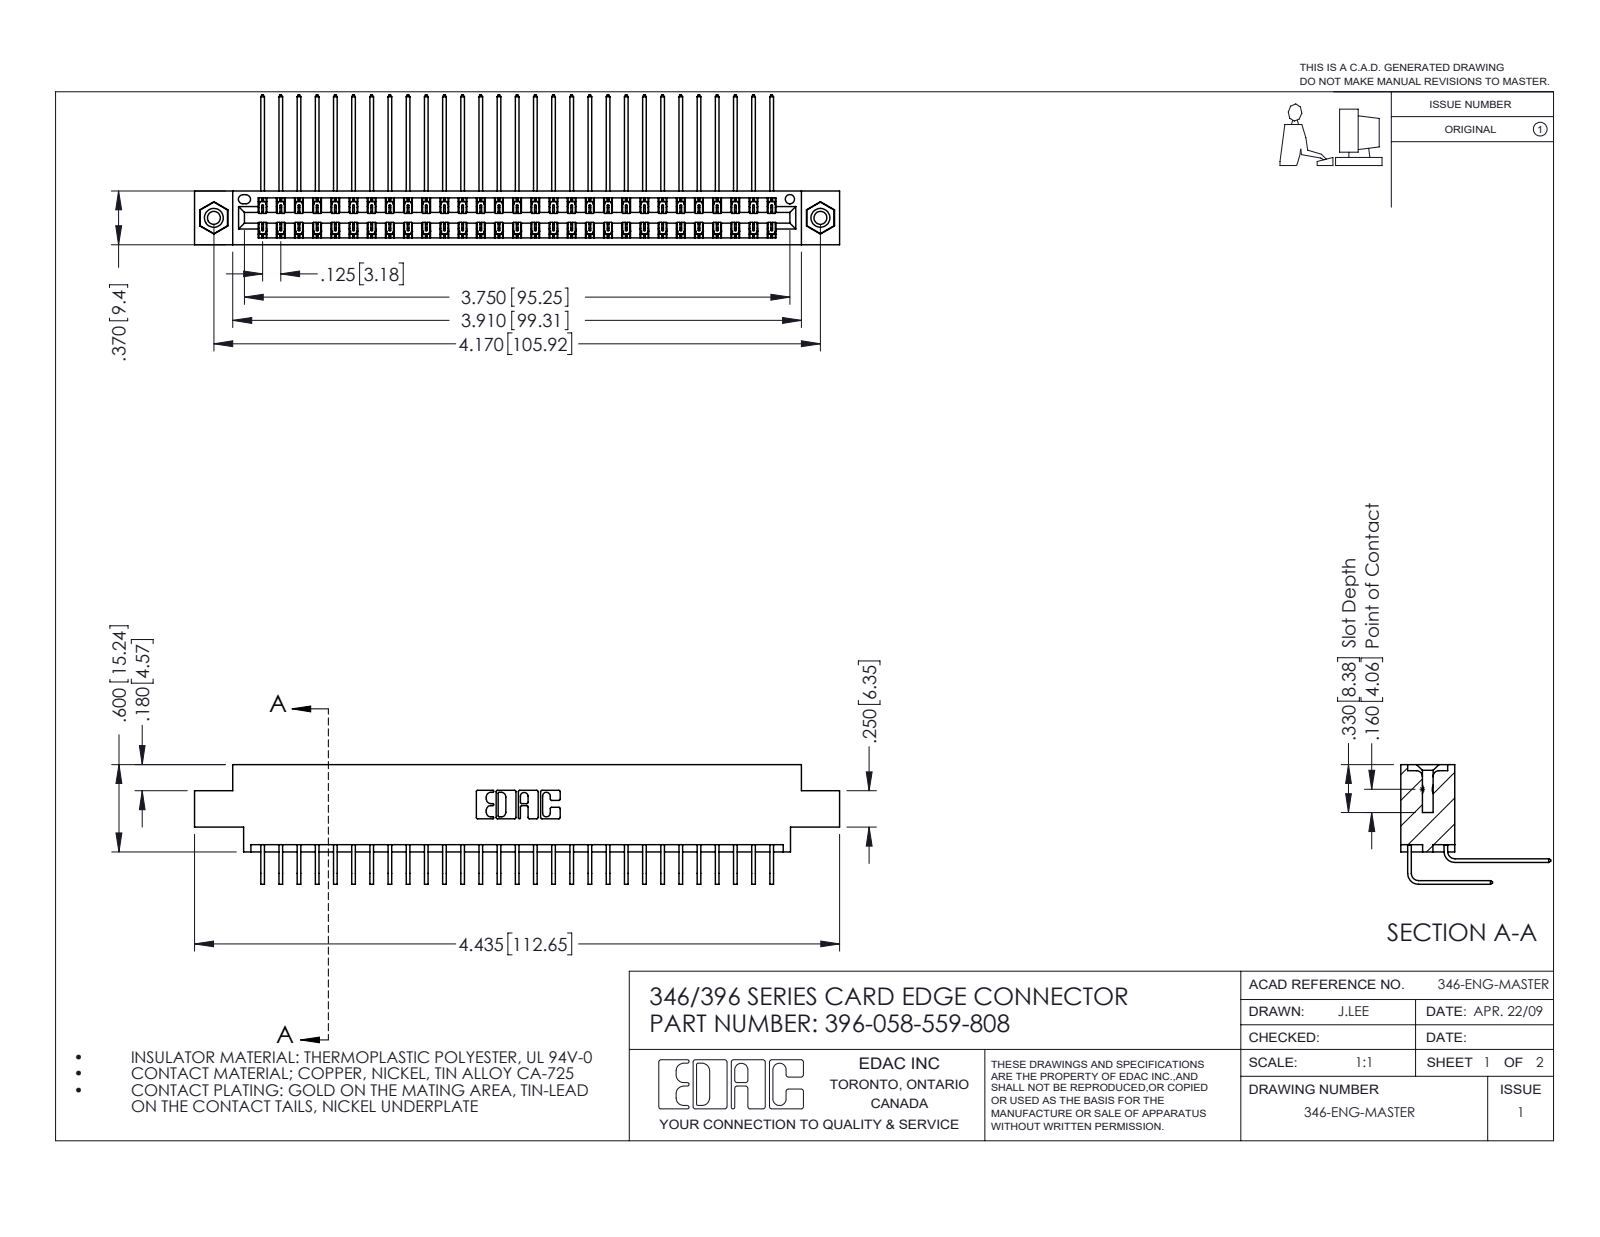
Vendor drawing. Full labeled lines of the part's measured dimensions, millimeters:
Part name (STEP PRODUCT): 346 Part_0.170 Offset - 0.156 Dia-TI; 396-058-559-808; 345-292-001_558 559 Tail - 1; 345-292-001_559 Tail - 2 (+1 more)
STEP written by: SolidWorks 2016 (CONFIG_CONTROL_DESIGN)
Units: millimetres
Bodies: 61 solids, 3318 faces (2258 planar, 1044 cylindrical, 16 other)
Overall size (bounding box): 112.6 × 26.2 × 20.9
Volume: 11 100 mm³ · Surface area: 16 800 mm²
Round holes (diameter × count): ⌀2.3 ×2, ⌀3.2 ×2, ⌀4 ×2, ⌀1.6 ×1
Round bosses / shafts (diameter × count): ⌀3.9 ×2
Partial cylindrical surfaces — rounded edges, fillets, slot ends (radius × count): R0.2 ×87, R0.3 ×22, R0.2 ×6, R0.8 ×6, R0.7 ×3, R0.4 ×2, R0.6 ×2, R0.6 ×2
Main face-to-face distances: 1.2, 8.2, 0.6, 9.4, 6.4, 1.8, 7.6, 7, 5.6, 3.8
Hole centre spacings: 6.2, 100.6, 105.9
